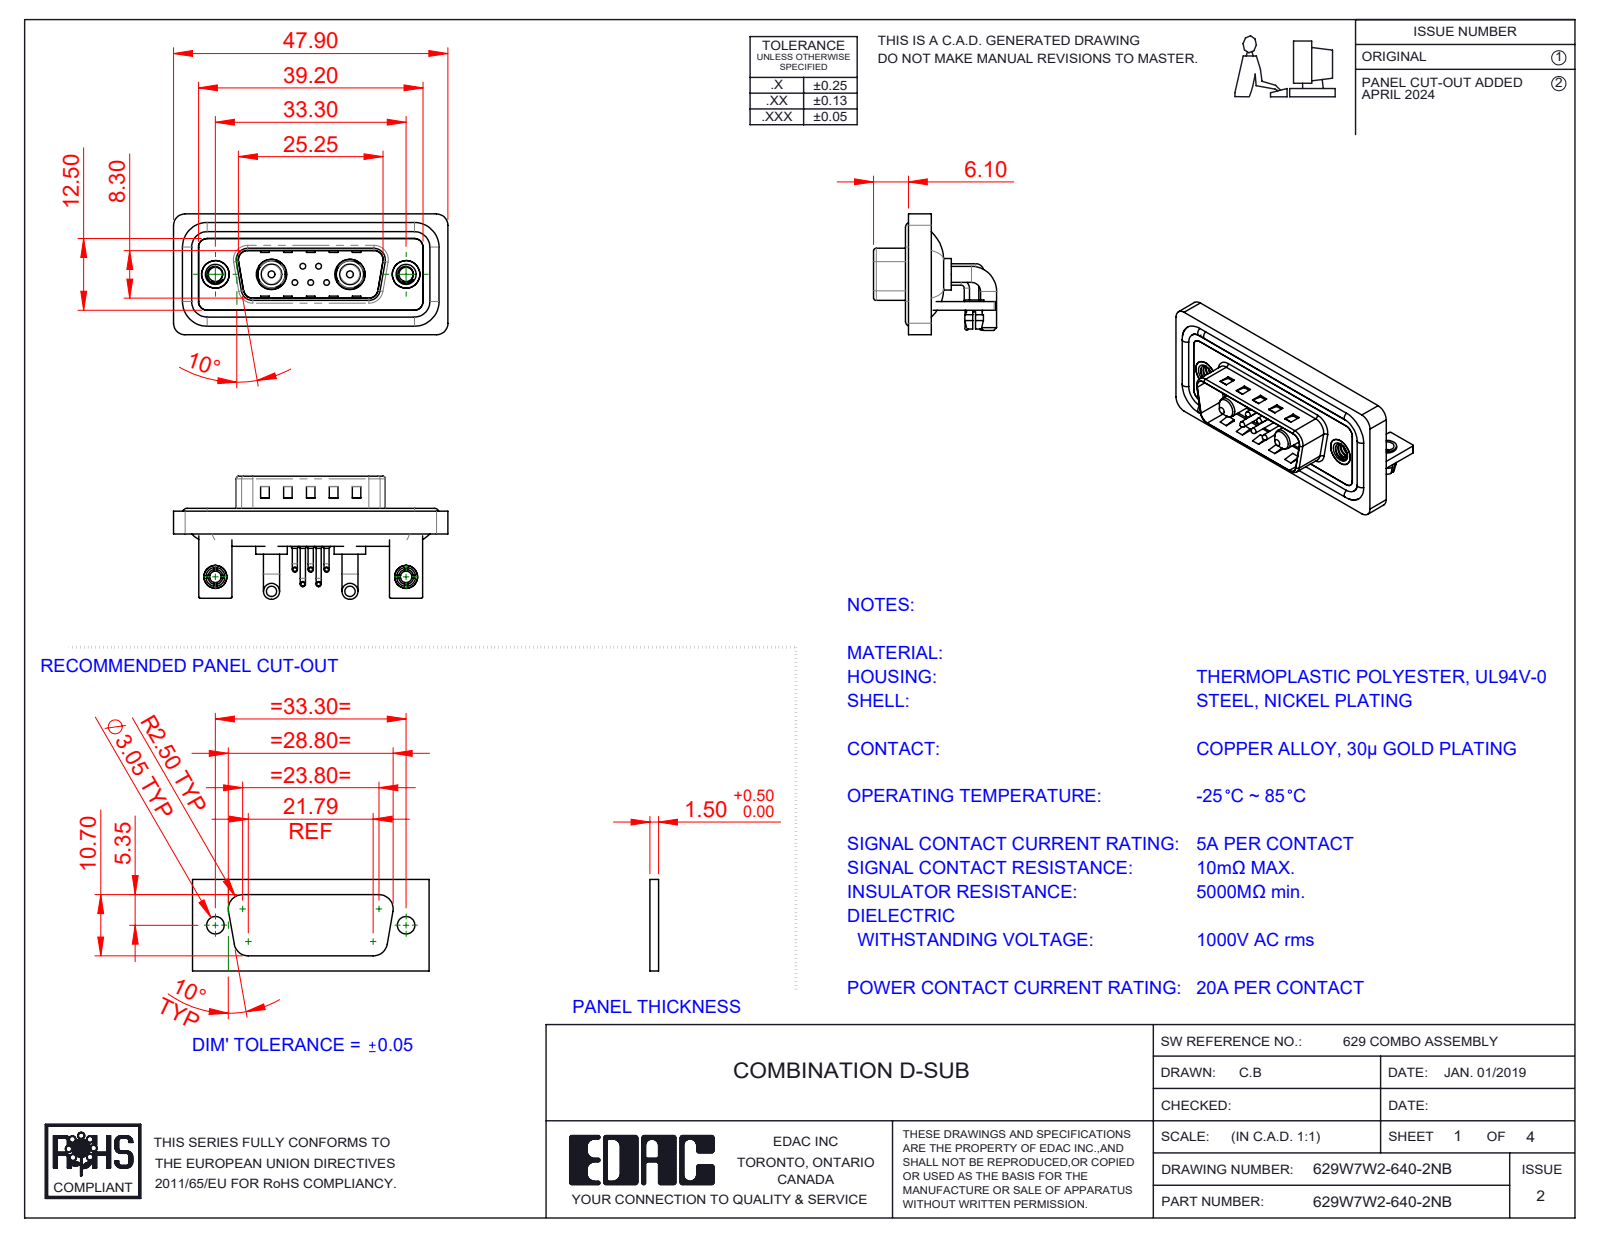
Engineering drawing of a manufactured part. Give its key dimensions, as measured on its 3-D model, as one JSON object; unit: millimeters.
{"part_name": "629Combo Waterproof Housing_15 Contacts; 629Combo Housing_7W2; 629Combo Stabilizer Bracket; 629Combo Contact Row 1 (+7 more)", "step_written_by": "SolidWorks 2023 (CONFIG_CONTROL_DESIGN)", "units": "millimeters", "bodies": {"solids": 20, "faces": 1213, "planar": 585, "cylindrical": 456, "other": 172}, "overall_size": [47.9, 21.5, 21.1], "volume_mm3": 5989, "surface_area_mm2": 9939, "round_holes": [[2, 7], [0.75, 5], [1.6, 5], [2.5, 4], [3.2, 2], [4, 2], [4.8, 2], [4.85, 2], [5, 2], [5.3, 2]], "round_bosses_or_shafts": [[0.9, 10], [1.5, 5], [1, 5], [0.65, 5], [2.8, 4], [1.6, 4], [5.5, 2], [5.2, 2]], "partial_cylinders_radius": [[2, 21], [1.5, 18], [0.25, 16], [0.5, 9], [1.6, 8], [1.01, 5], [0.6, 4], [0.65, 4]], "face_to_face_distances": [0.4, 1.5, 0.8, 2.9, 2.1, 1.1, 1.6, 1.2, 3.7, 4.5], "hole_center_spacings": [3.16, 2.77, 9.8, 23.5, 33.3, 4.31, 4.33, 5.03]}
